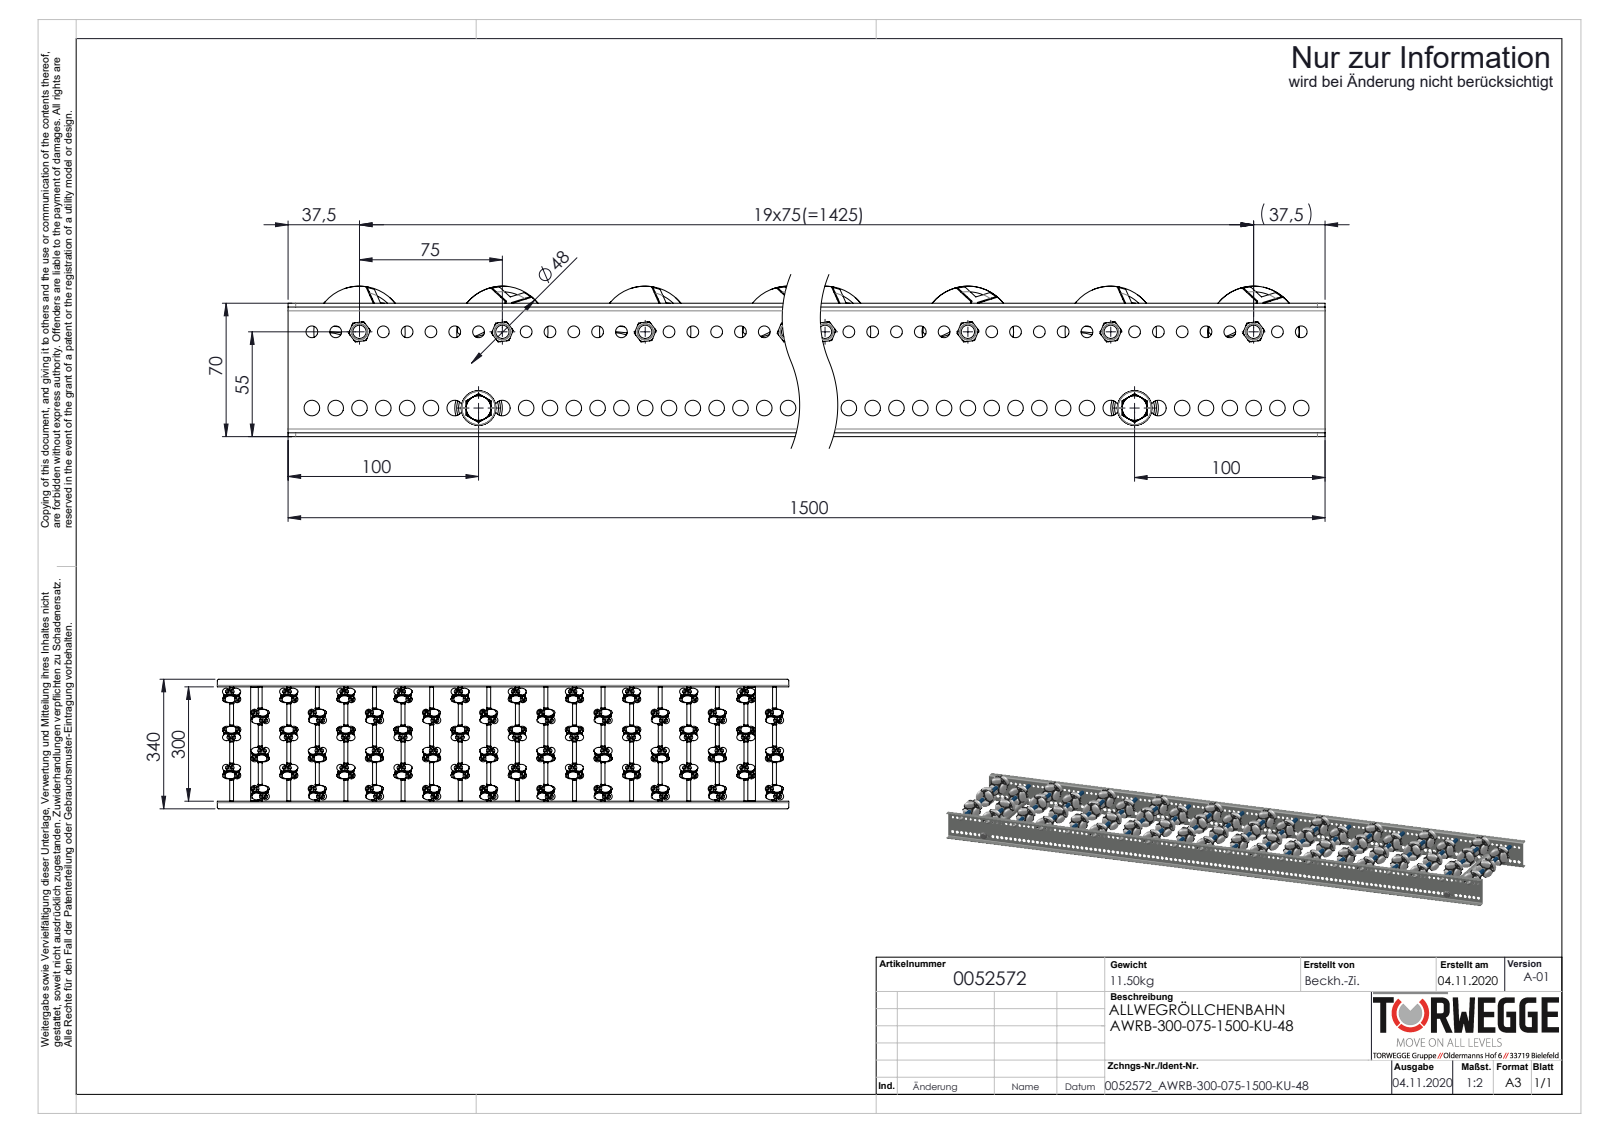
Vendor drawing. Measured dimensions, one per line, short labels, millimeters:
name: 0015028_AWR48; 0019730_Tragrollenrohr-Ø10x1,75KU_KFG_0019730_L=55; 0027528_BUCHSE-HOHLNIETE ZU AWR48; AWR-Achse-für-Konfiguration_L300 (+8 more)
written by: SolidWorks 2020 (AUTOMOTIVE_DESIGN)
unit: mm
bodies: 1032 solids, 18872 faces (6360 planar, 7448 cylindrical, 5064 other)
size: 1500 × 340 × 79
volume: 3 594 000 mm³; area: 2 543 000 mm²
holes: 360× ⌀3.7, 360× ⌀4.2, 119× ⌀6.2, 119× ⌀8.2, 20× ⌀4.92, 20× ⌀6.5, 20× ⌀8.4, 2× ⌀6.8, 2× ⌀21
bosses: 360× ⌀4, 328× ⌀3.7, 22× ⌀8, 20× ⌀42, 20× ⌀11, 20× ⌀10, 20× ⌀7, 20× ⌀6
rounds: 20× R23.55, 8× R4, 4× R2
face distances: 2, 302, 68, 300, 304, 70, 66, 3, 20, 5
hole spacings: 36.06, 36.05, 33.16, 108.88, 143.46, 61.38, 109.68, 6
